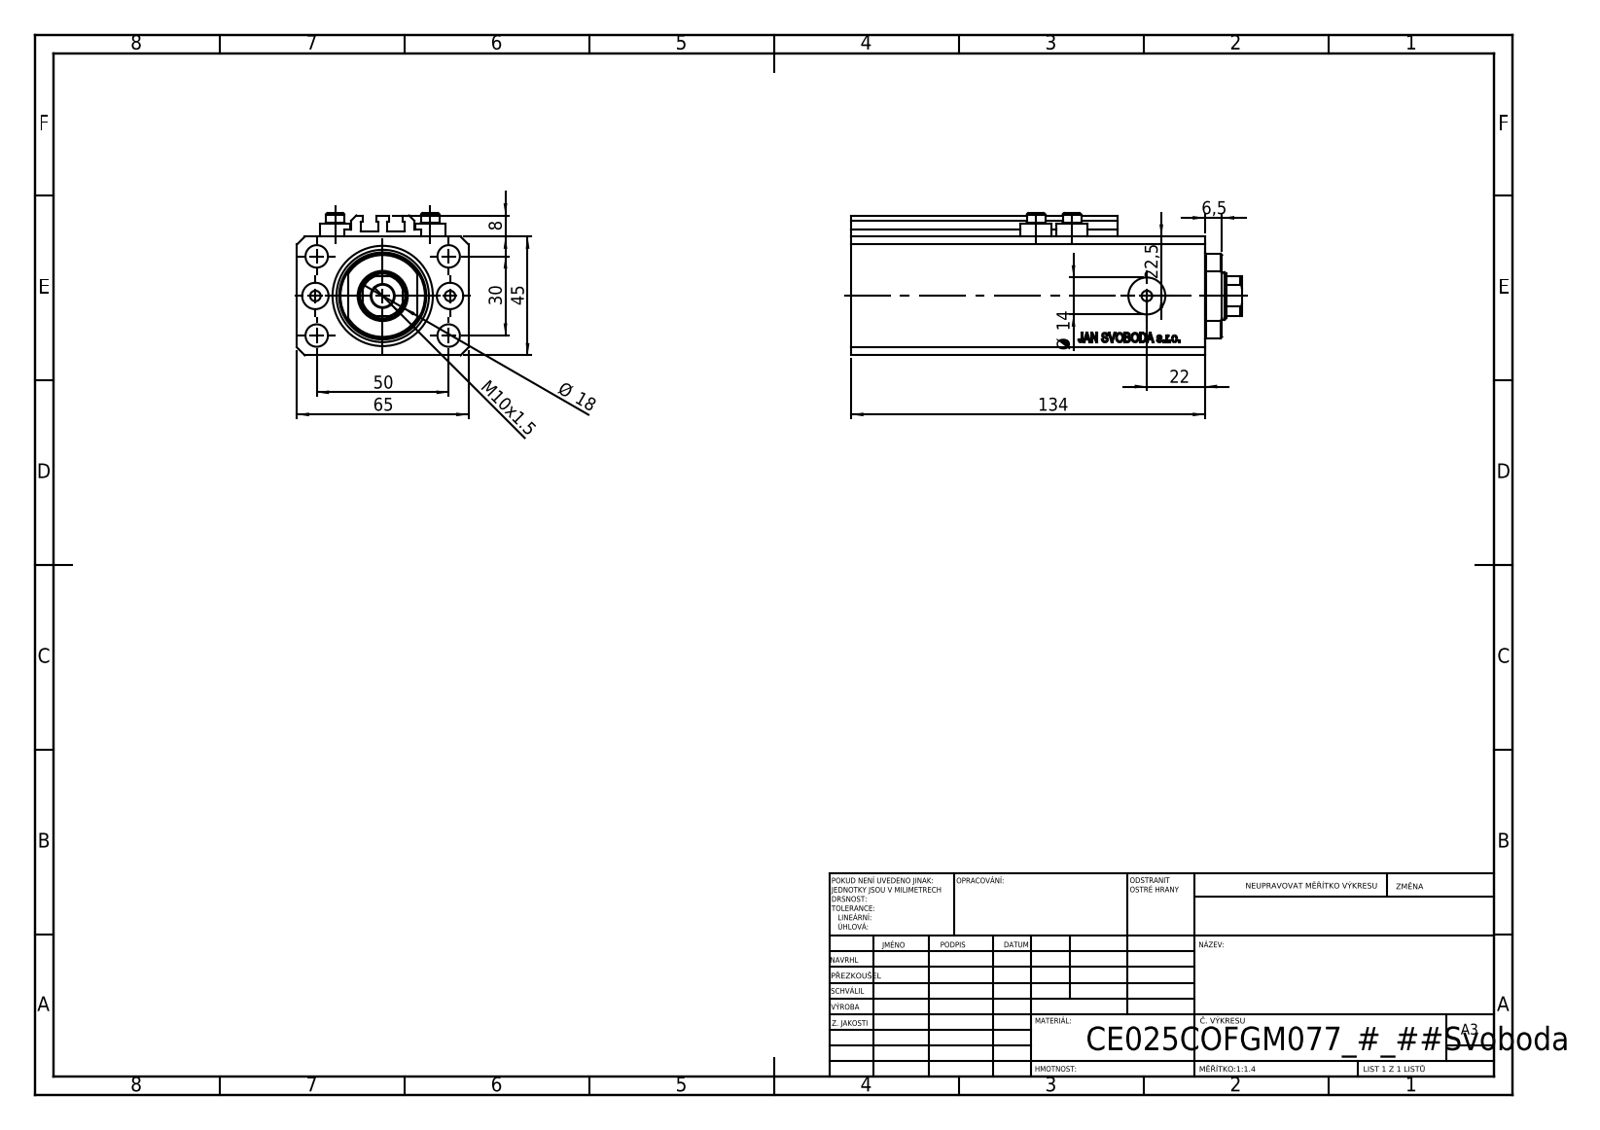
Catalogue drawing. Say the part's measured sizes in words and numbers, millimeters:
The part is named "V250CE_VC_C; V250CE_C_VCP; ALLEN BOLT V250CE; V250CE_C_Body". Its 3-D file was written by "SolidWorks 2019 (CONFIG_CONTROL_DESIGN)". It is 8 solids with 1034 faces: 504 planar, 86 cylindrical and 444 other. Overall it measures 148 by 65 by 54 millimeters. Its volume is 358 417 cubic millimeters and its surface area 88 939 square millimeters. Round holes: 8 of diameter 4, 5 of diameter 8.5, 2 of diameter 10, 2 of diameter 14, 1 of diameter 18, 1 of diameter 25, 1 of diameter 38. Round bosses or shafts: 4 of diameter 11.6, 4 of diameter 7. Partial cylindrical surfaces (rounded edges, fillets, slot ends): 10 of radius 0.2, 1 of radius 8.5, 1 of radius 16. The main face-to-face distances are 45, 65, 47, 14, 120, 134, 2.5, 2, 10, 20.5. The hole center spacings are 15.01, 29.15, 52.68, 13.6, 25.5, 30, 36, 38.48.
